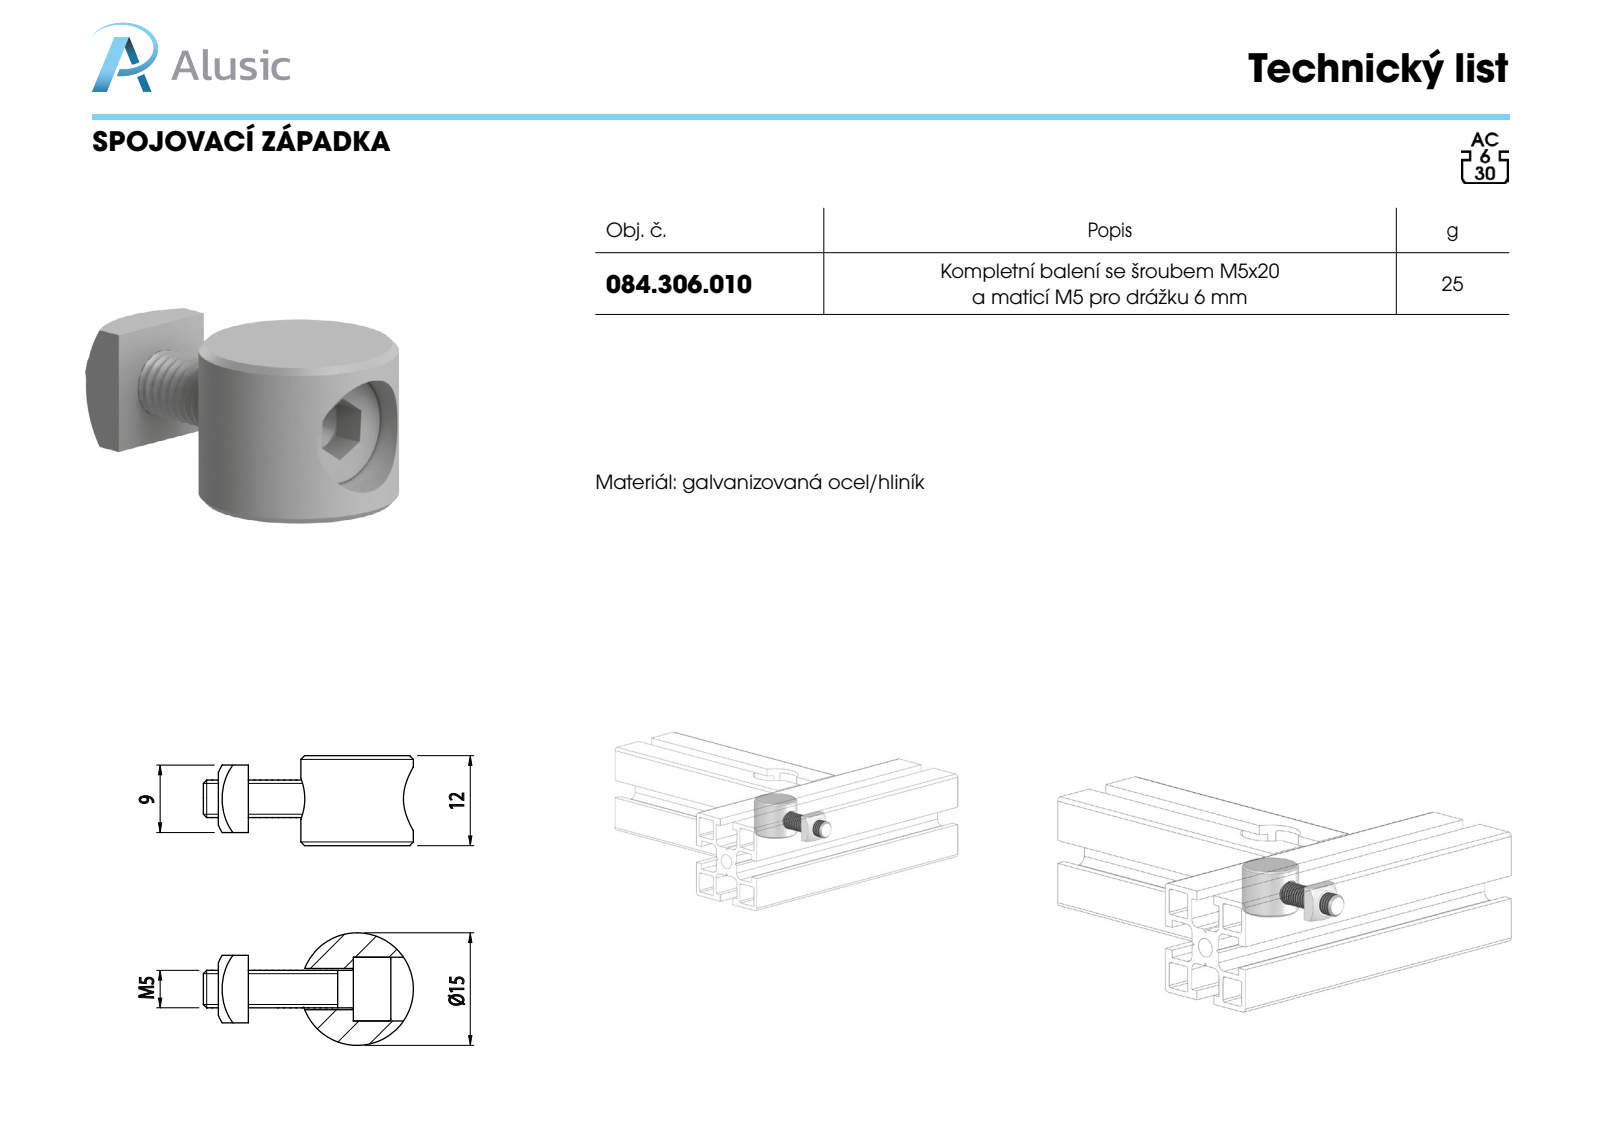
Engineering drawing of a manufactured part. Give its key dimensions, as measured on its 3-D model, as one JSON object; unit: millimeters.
{"part_name": "084.306.010", "step_written_by": "SolidWorks 2011 (CONFIG_CONTROL_DESIGN)", "units": "millimeters", "bodies": {"solids": 1, "faces": 13, "planar": 3, "cylindrical": 6, "other": 4}, "overall_size": [15, 15, 12], "volume_mm3": 1510, "surface_area_mm2": 1153, "round_holes": [[5.5, 1], [8.5, 1]], "round_bosses_or_shafts": [[15, 1]], "face_to_face_distances": [12]}
